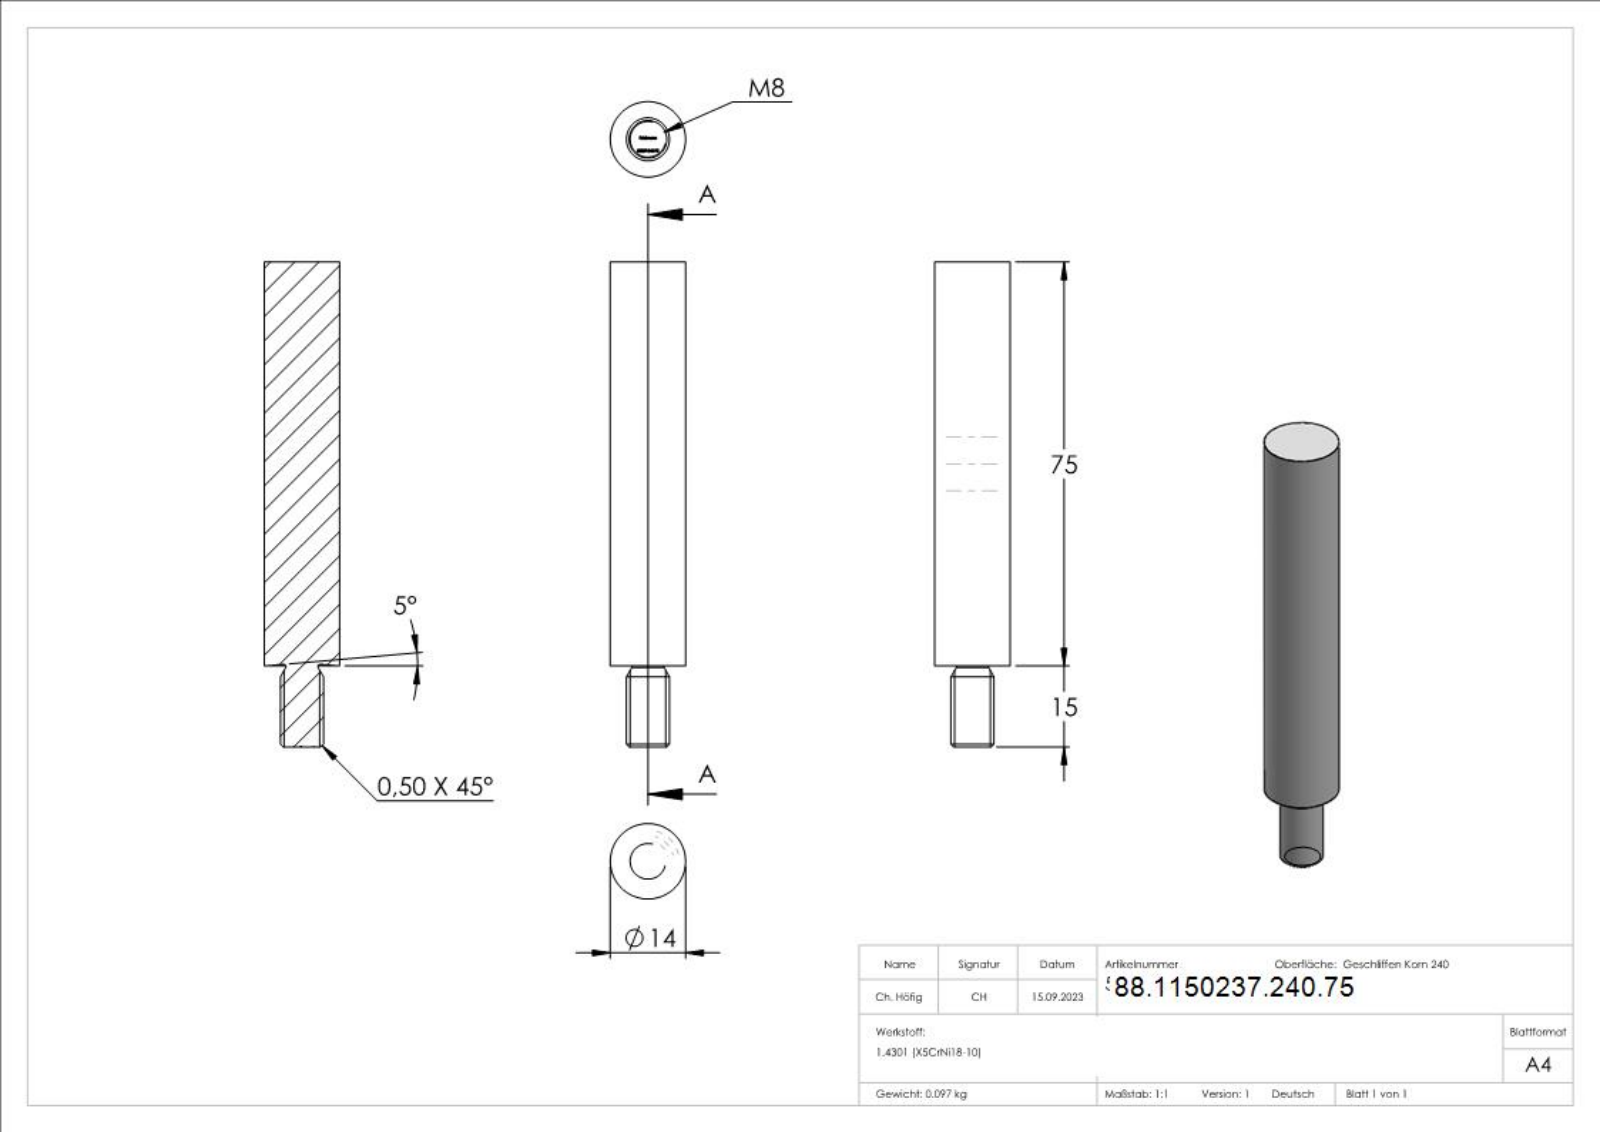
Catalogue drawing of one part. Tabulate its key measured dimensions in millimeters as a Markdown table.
| quantity | value |
| --- | --- |
| part name | 50237-240-75 |
| STEP written by | SolidWorks 2018 (CONFIG_CONTROL_DESIGN) |
| units | millimeters |
| bodies | 1 solid, 256 faces (142 planar, 2 cylindrical, 112 other) |
| overall size | 90 × 14 × 14 |
| volume | 12 252 mm³ |
| surface area | 4 005 mm² |
| round bosses / shafts (diameter × count) | 14 × 1, 8 × 1 |
| main face-to-face distances | 90, 89.9, 1.5, 0.53, 0.57, 0.47, 2.38, 0.35, 0.62, 2.44 |
